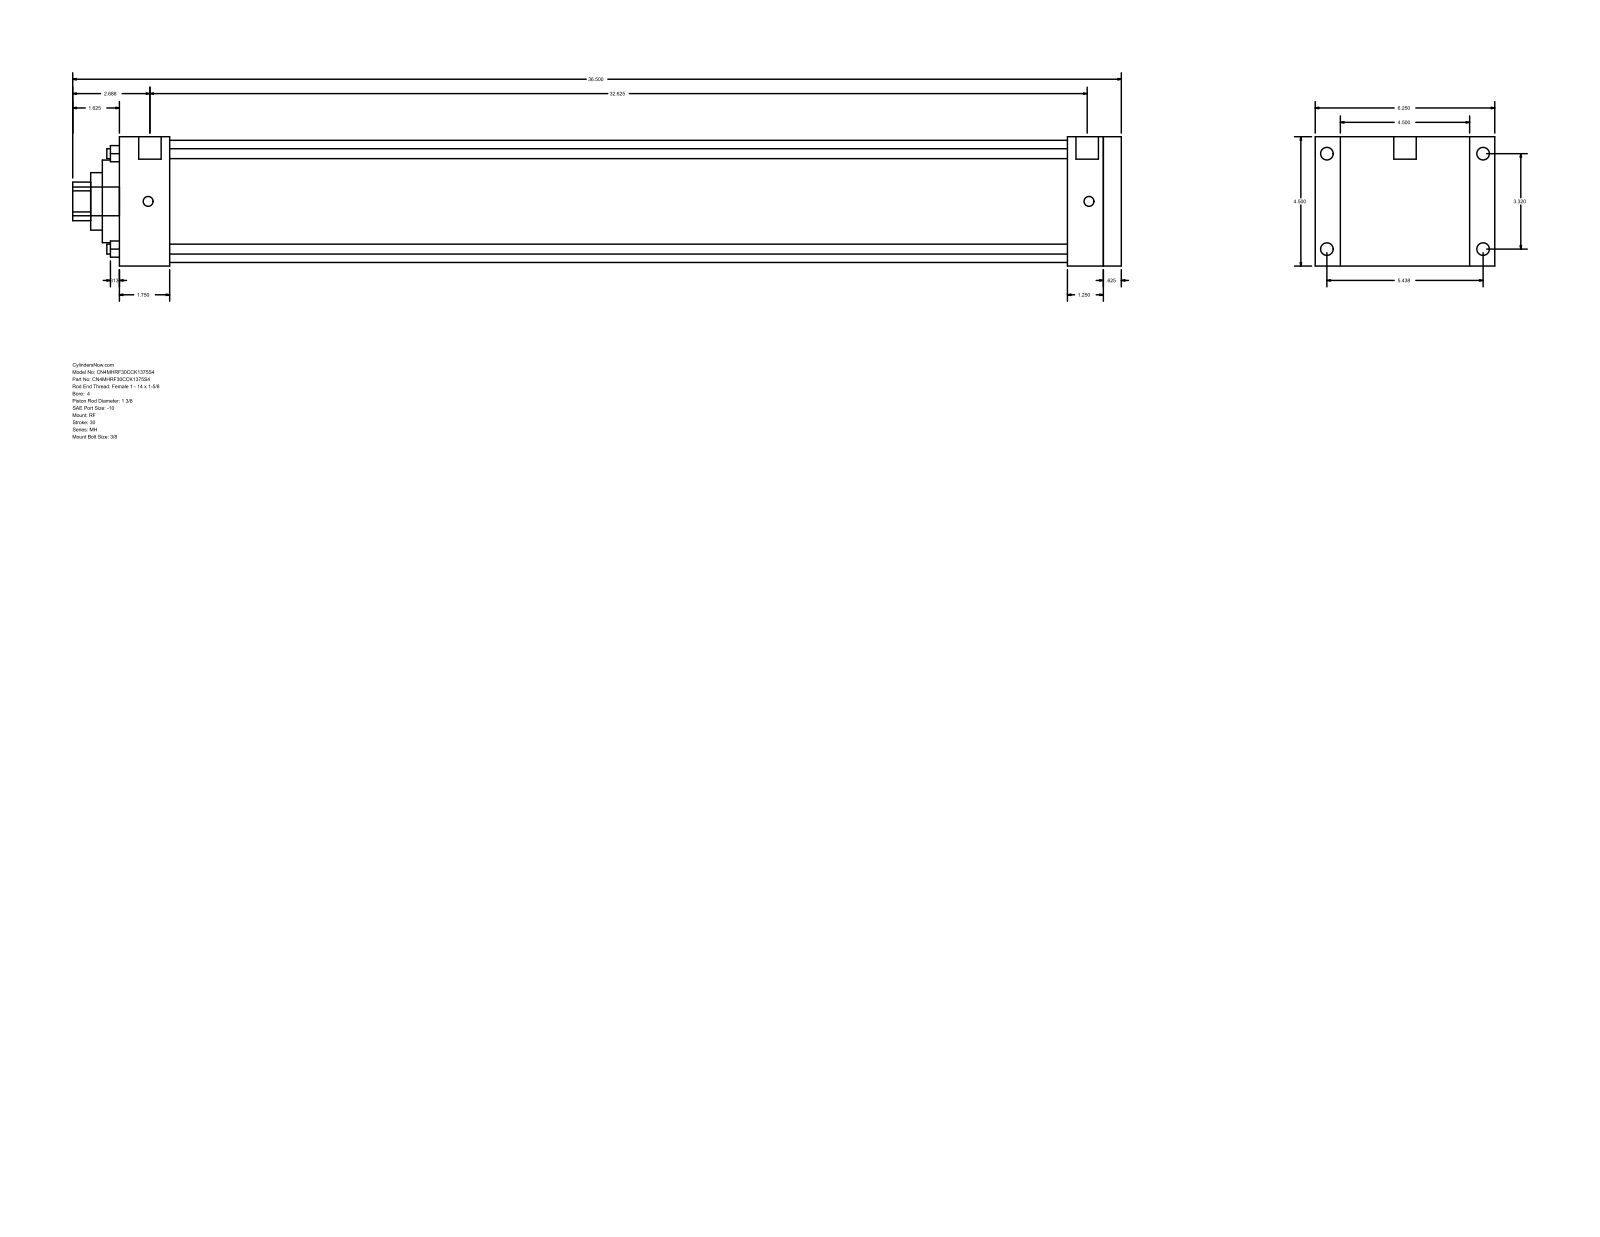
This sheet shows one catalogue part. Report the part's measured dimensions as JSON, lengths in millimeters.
{"part_name": "MH_RF__0400_1.375", "step_written_by": "GSSL Pune (CONFIG_CONTROL_DESIGN)", "units": "millimeters", "bodies": {"solids": 0, "faces": 94, "planar": 65, "cylindrical": 29, "other": 0}, "overall_size": [927.1, 158.75, 114.3], "round_holes": [[8.76, 4], [34.92, 1], [50.8, 1], [73.03, 1], [107.95, 1]], "round_bosses_or_shafts": [[11.13, 4], [8.73, 4], [19.84, 2], [25.4, 1]], "partial_cylinders_radius": [[17.06, 1]], "face_to_face_distances": [114.3, 885.83, 869.96, 15.87, 44.45, 825.51, 841.38, 838.21, 793.76, 31.75], "hole_center_spacings": [59.62, 84.32, 119.25]}
